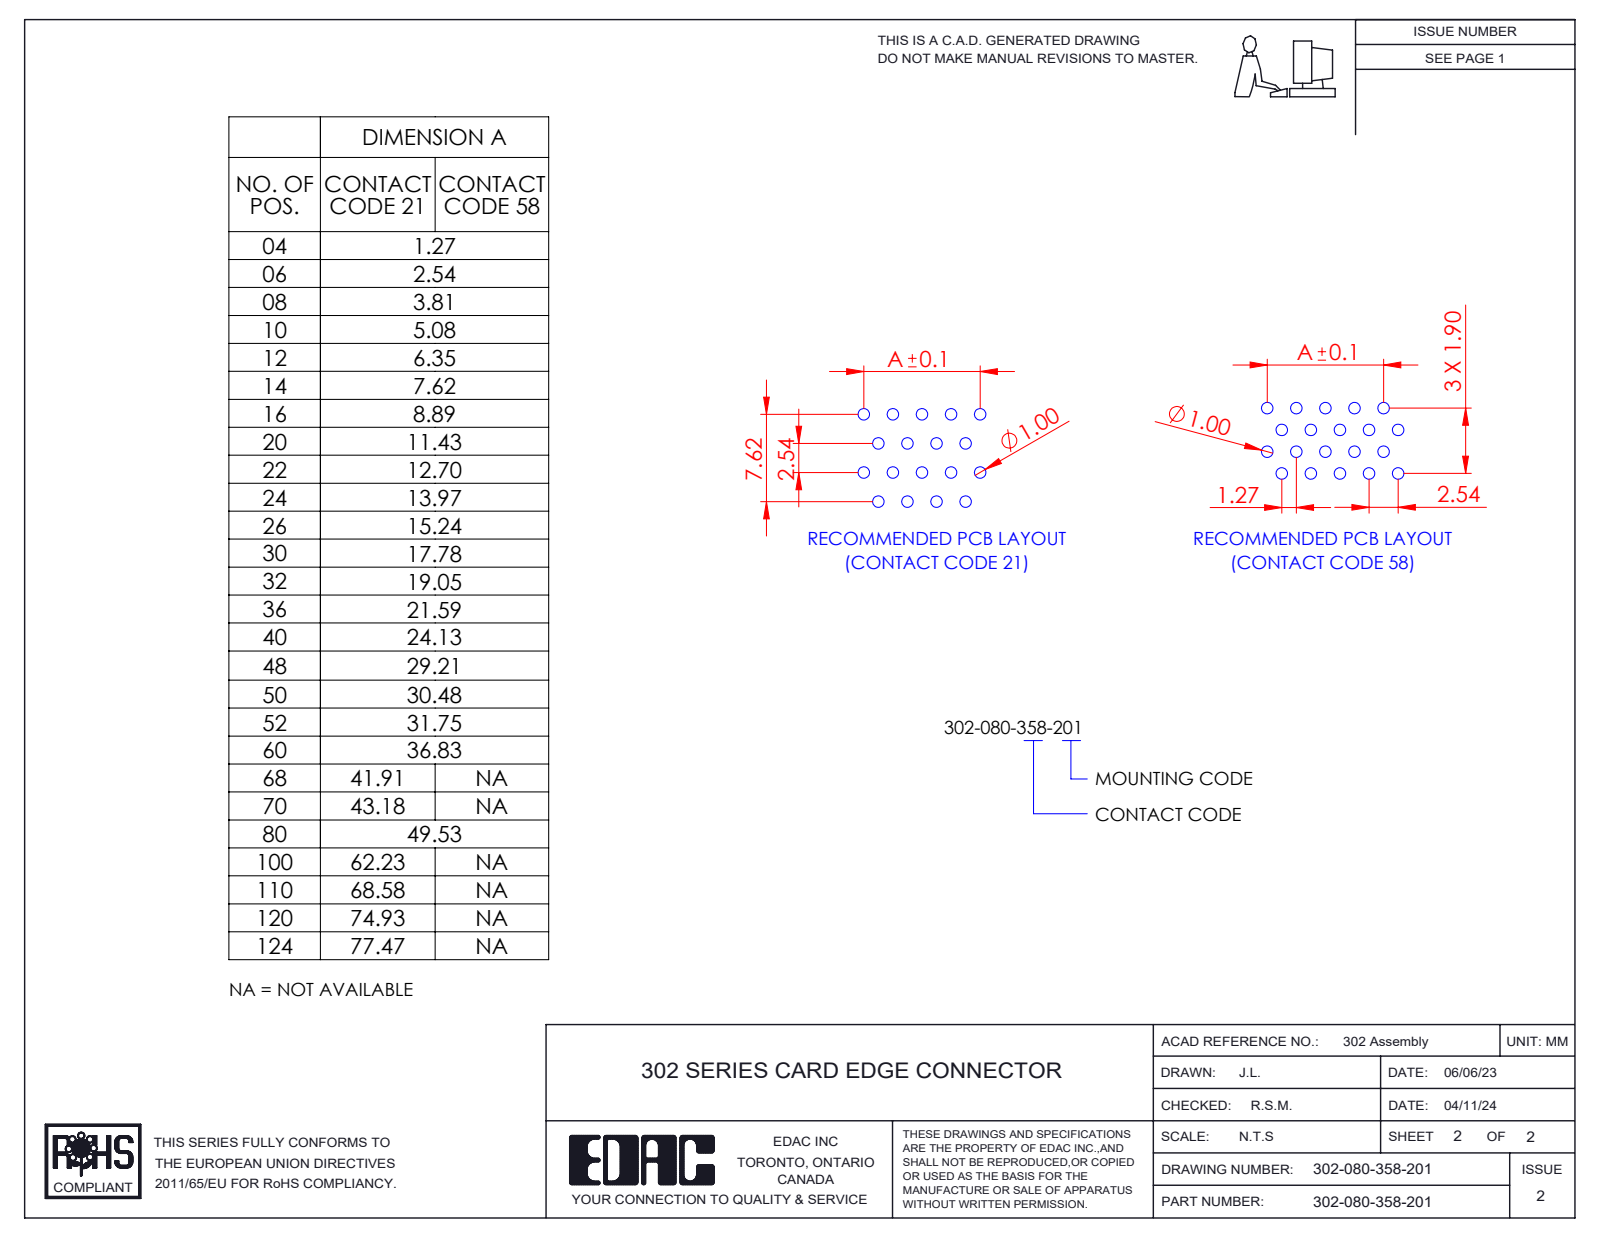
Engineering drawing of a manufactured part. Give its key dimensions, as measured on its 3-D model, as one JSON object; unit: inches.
{"part_name": "302-080-358-201; Contact_302-290-X58-001; Contact_302-290-X58-003; HSG_RA HSG (80P) (+2 more)", "step_written_by": "SolidWorks 2023 (CONFIG_CONTROL_DESIGN)", "units": "inches", "bodies": {"solids": 81, "faces": 4227, "planar": 3007, "cylindrical": 1056, "other": 164}, "overall_size": [2.24, 0.841, 0.46], "volume_in3": 0.307, "surface_area_in2": 22.37, "partial_cylinders_radius": [[0.008, 88], [0.01, 80], [0.02, 4], [0.08, 3], [0.004, 2], [0.016, 2], [0.016, 2], [0.031, 2]], "face_to_face_distances": [0.05, 0.1, 0.15, 0.2, 0.075, 0.3, 0.25, 0.35, 0.35, 0.4]}
